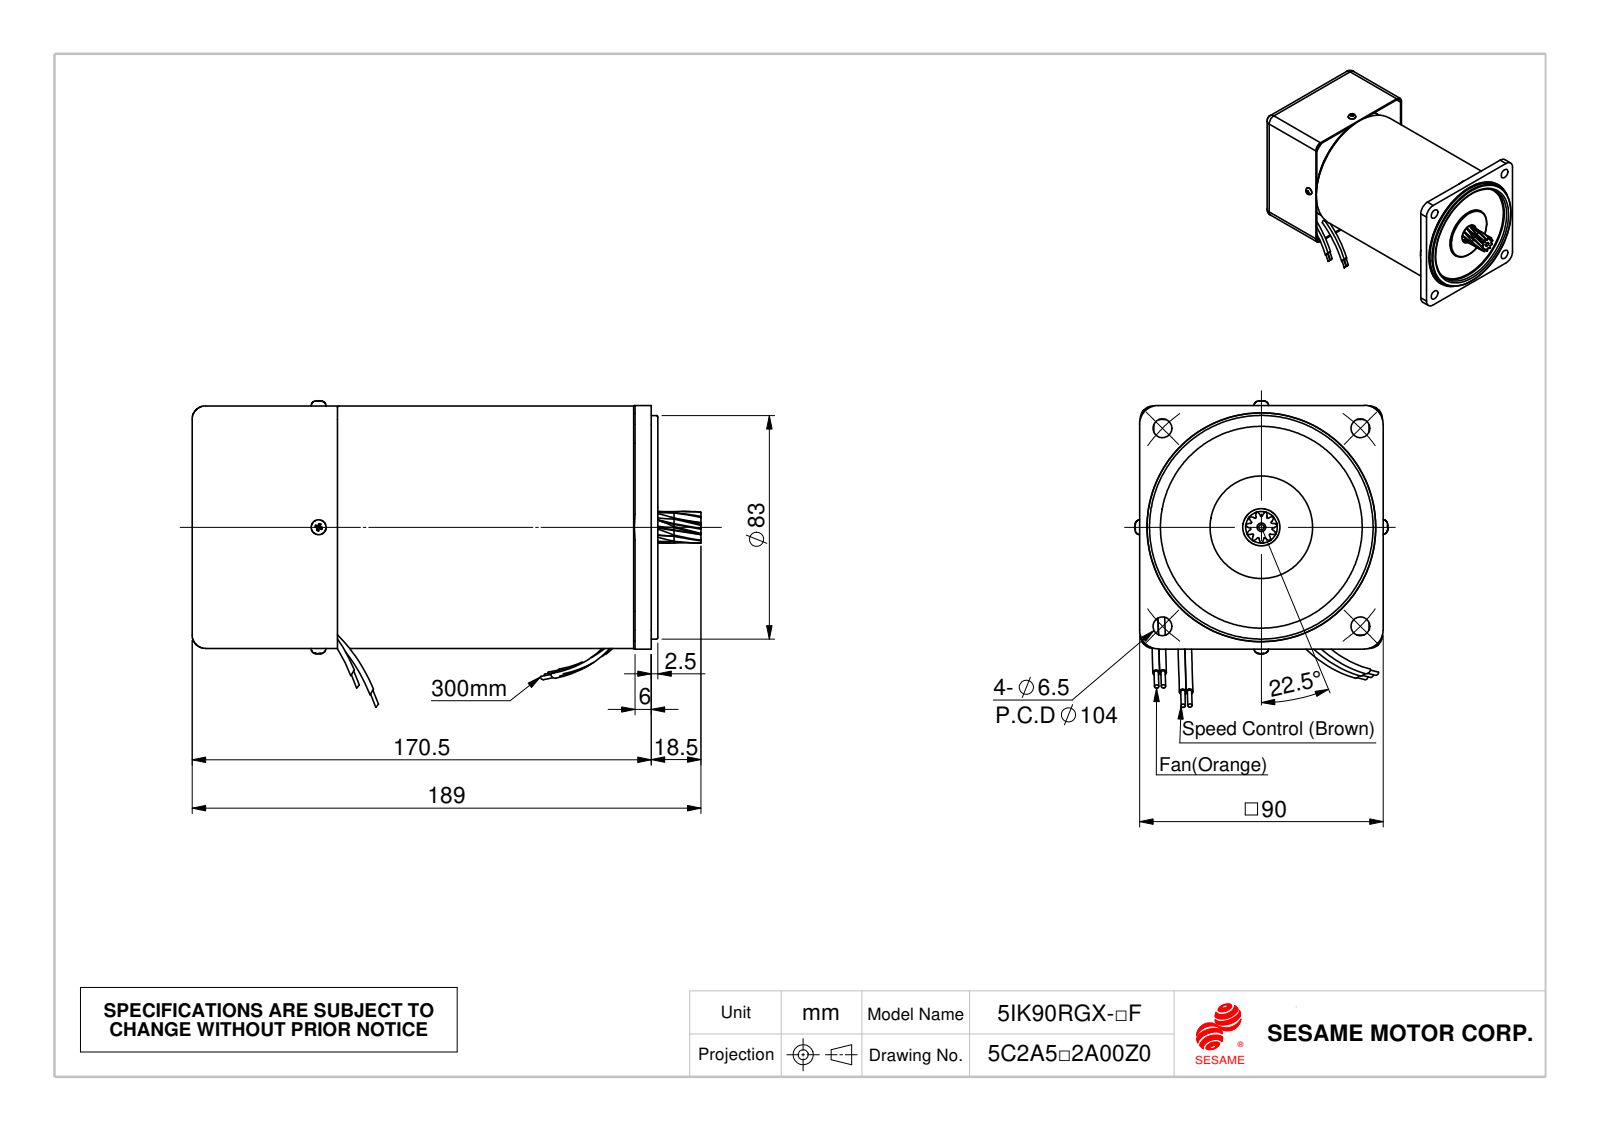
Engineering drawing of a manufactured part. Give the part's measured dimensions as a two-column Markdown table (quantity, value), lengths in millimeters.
| quantity | value |
| --- | --- |
| part name | 90GX_1成品; M590-R-F; 獨立風扇220V 3K22200000 |
| STEP written by | SolidWorks 2010 (CONFIG_CONTROL_DESIGN) |
| units | millimeters |
| bodies | 15 solids, 509 faces (169 planar, 171 cylindrical, 169 other) |
| overall size | 189 × 113.87 × 93.92 |
| volume | 1 048 000 mm³ |
| surface area | 136 707 mm² |
| round holes (diameter × count) | 2.5 × 5, 7 × 4, 3 × 2, 2 × 1, 9.5 × 1, 13.7 × 1, 16 × 1, 26 × 1, 58.1 × 1, 64.97 × 1, 75 × 1, 84.4 × 1 |
| round bosses / shafts (diameter × count) | 11 × 3, 5.5 × 2, 90 × 1, 87 × 1, 86 × 1, 84.15 × 1, 84 × 1, 83 × 1 |
| partial cylindrical surfaces (radius × count) | 0.3 × 16, 4 × 8, 5 × 8, 2 × 4, 7 × 4, 26.9 × 1, 44.58 × 1 |
| main face-to-face distances | 1, 89, 4, 5, 84, 85, 90, 88, 139.9, 29 |
| hole center spacings | 38.18, 52, 73.18, 73.54, 26.5, 104, 53, 123.54 |
